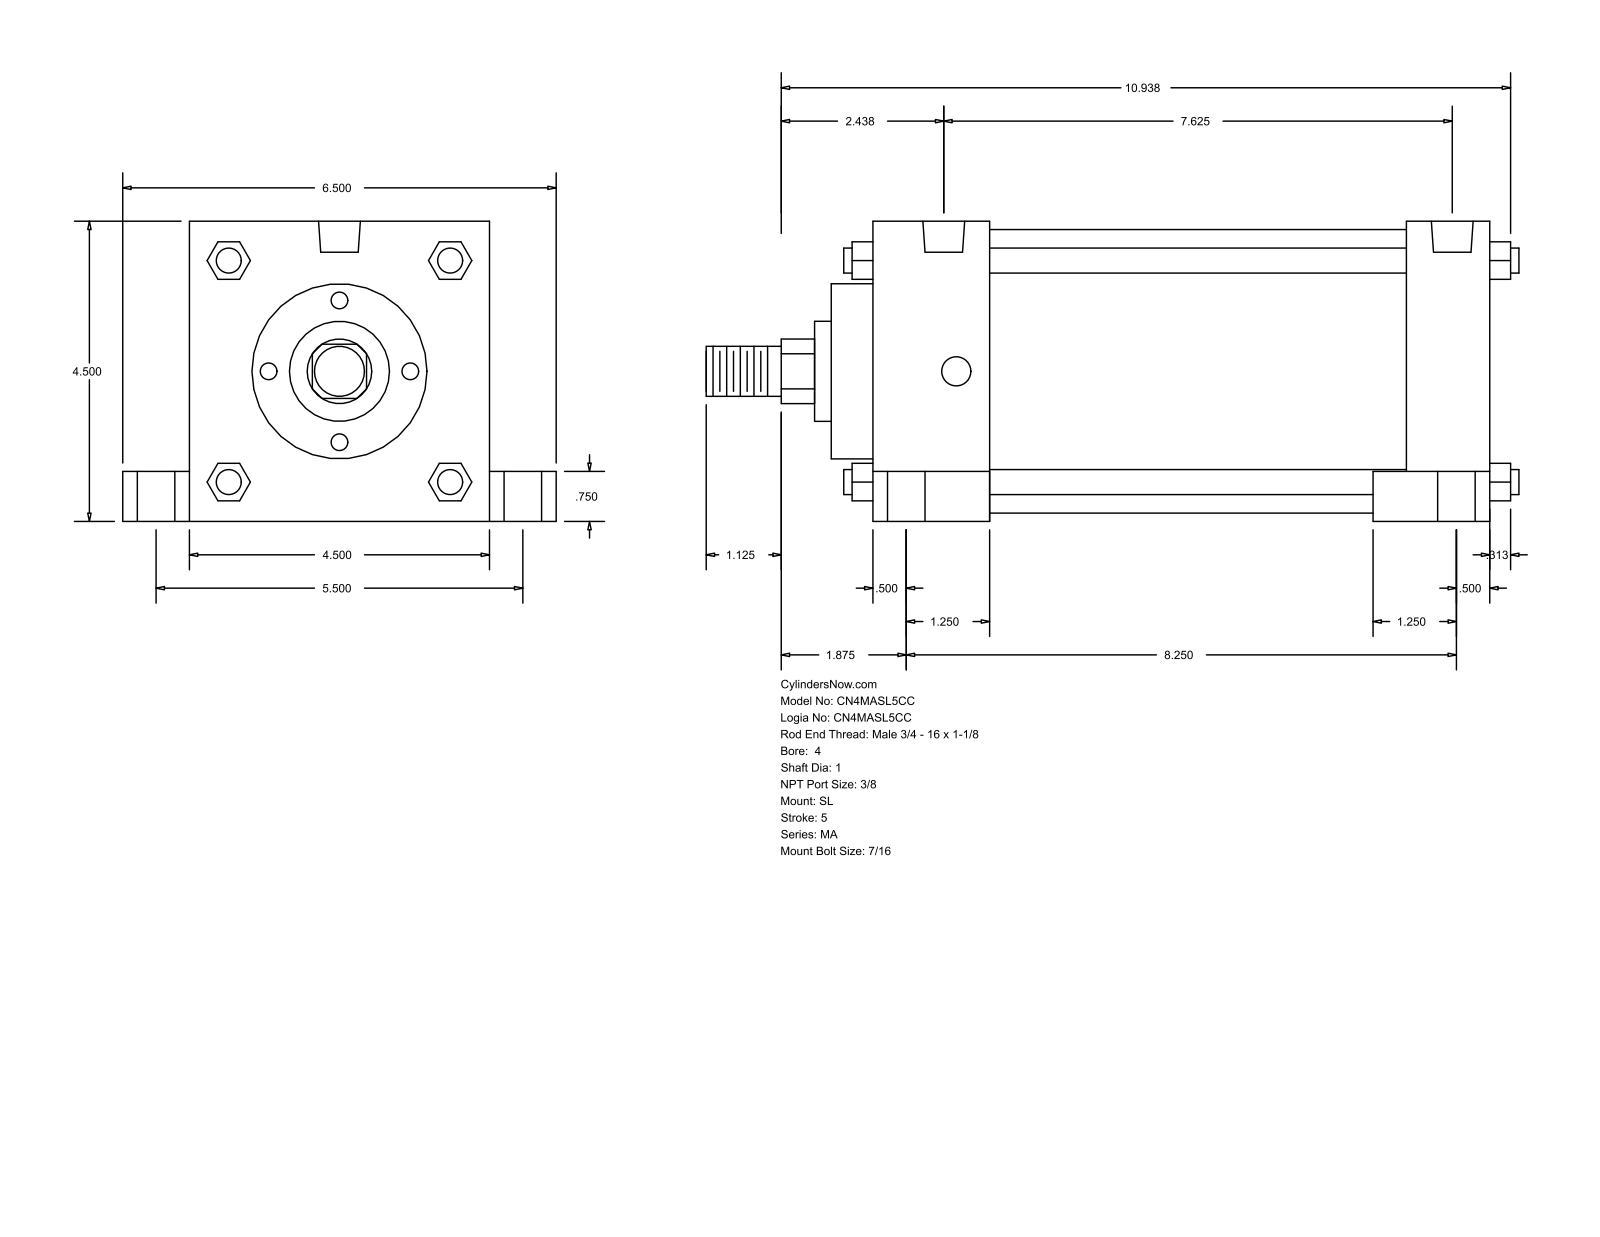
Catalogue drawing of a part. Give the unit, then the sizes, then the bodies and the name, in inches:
Units: inches
Overall size (bounding box): 12.187 × 6.5 × 4.5
Round holes (diameter × count): ⌀0.437 ×4, ⌀0.563 ×4, ⌀0.813 ×4, ⌀0.627 ×2
Round bosses / shafts (diameter × count): ⌀0.375 ×4, ⌀4.25 ×1, ⌀2.625 ×1, ⌀1.5 ×1, ⌀1 ×1, ⌀0.75 ×1
Partial cylindrical surfaces — rounded edges, fillets, slot ends (radius × count): R0.484 ×1
Main face-to-face distances: 4.5, 9.25, 1.75, 7.5, 8, 6.25, 1.25, 1, 5.5, 0.75
Hole centre spacings: 2.751, 2.761, 2.807, 2.85, 5.5, 7.25, 7.989, 8.165
Bodies: 0 solids, 150 faces (113 planar, 37 cylindrical, 0 other)
Part name (STEP PRODUCT): MA_SL__0400_1
STEP written by: GSSL Pune (CONFIG_CONTROL_DESIGN)
